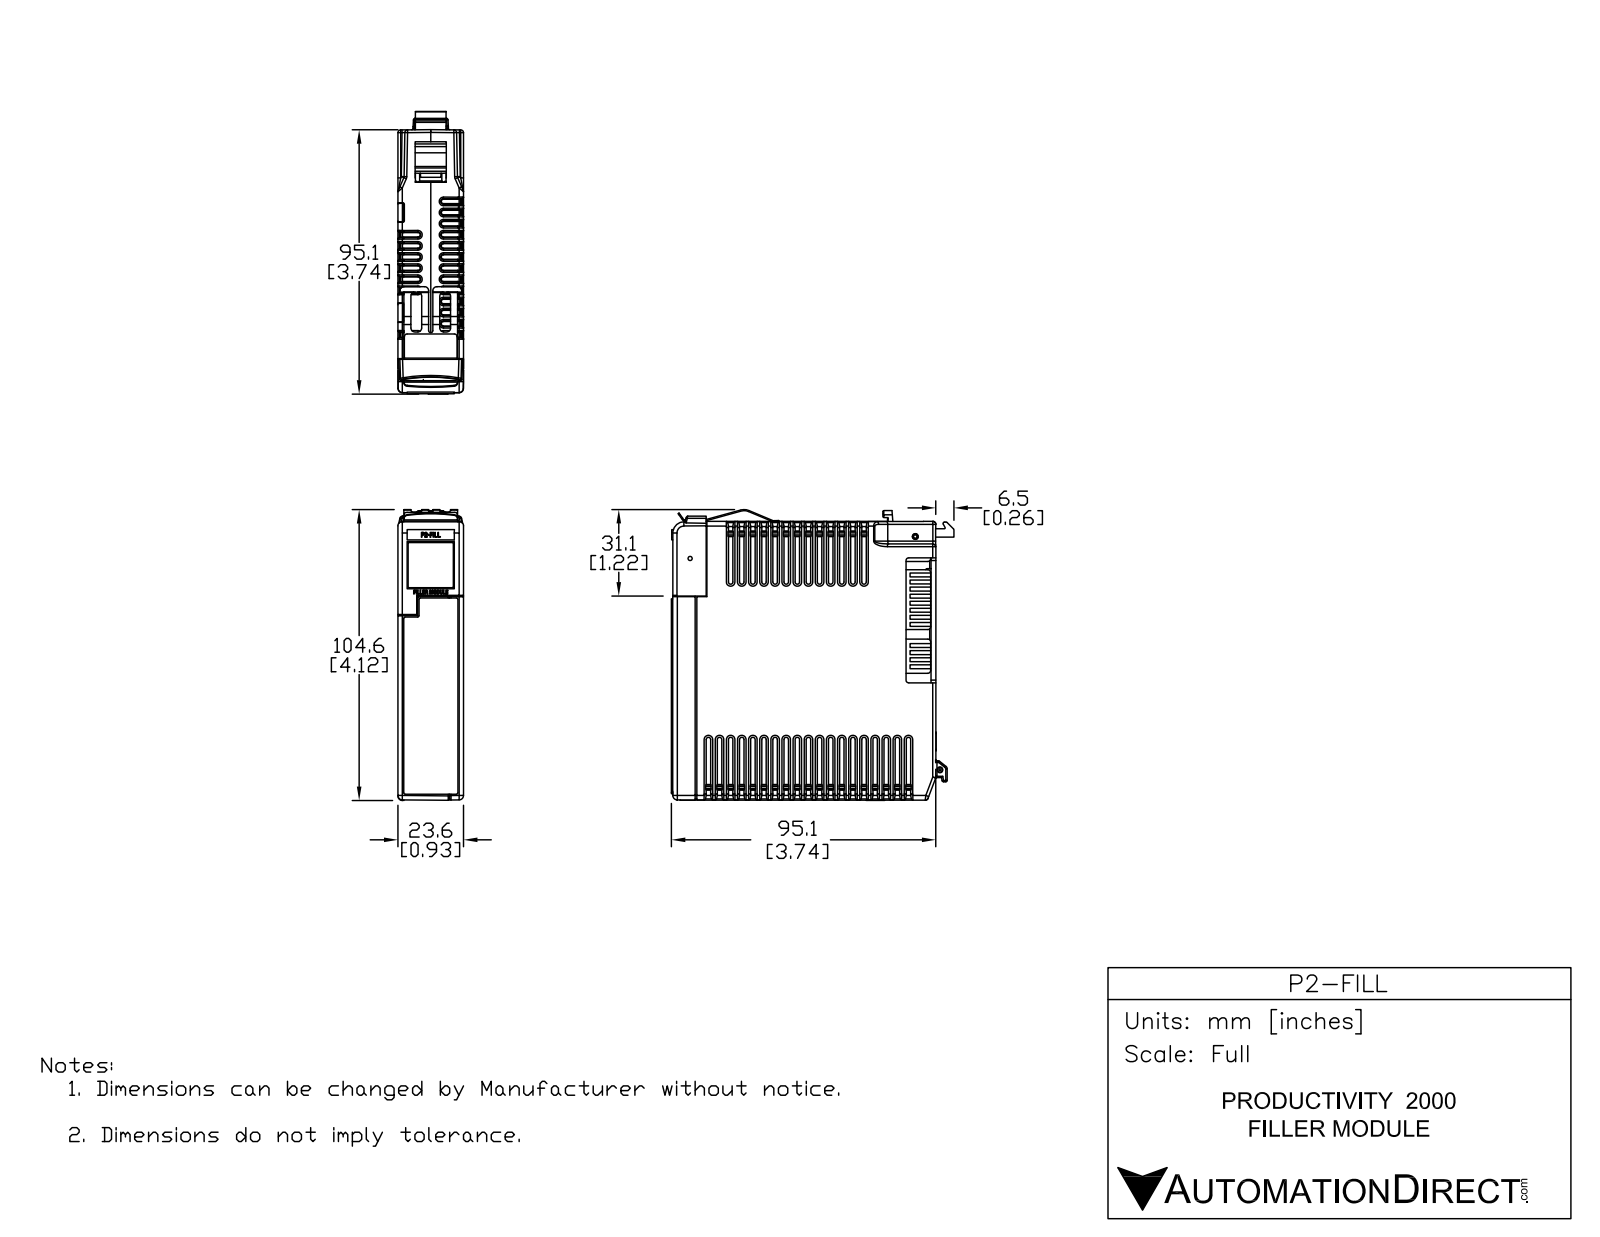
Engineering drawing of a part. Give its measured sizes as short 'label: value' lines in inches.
name: P2-FILL
written by: SolidWorks 2017 (AUTOMOTIVE_DESIGN)
unit: in
bodies: 7 solids, 3616 faces (1621 planar, 1012 cylindrical, 983 other)
size: 4.107 × 4.001 × 0.93
volume: 2.279 in³; area: 94.47 in²
holes: 1× ⌀0.059, 1× ⌀0.079, 1× ⌀0.083, 1× ⌀0.098
rounds: 443× R0.02, 89× R0.039, 43× R0.008, 22× R0.059, 12× R0.063, 8× R0.016, 6× R0.079, 4× R0.053
face distances: 0.063, 0.867, 0.804, 0.93, 0.154, 0.309, 0.015, 3.661, 3.676, 3.948
hole spacings: 3.206, 3.206
